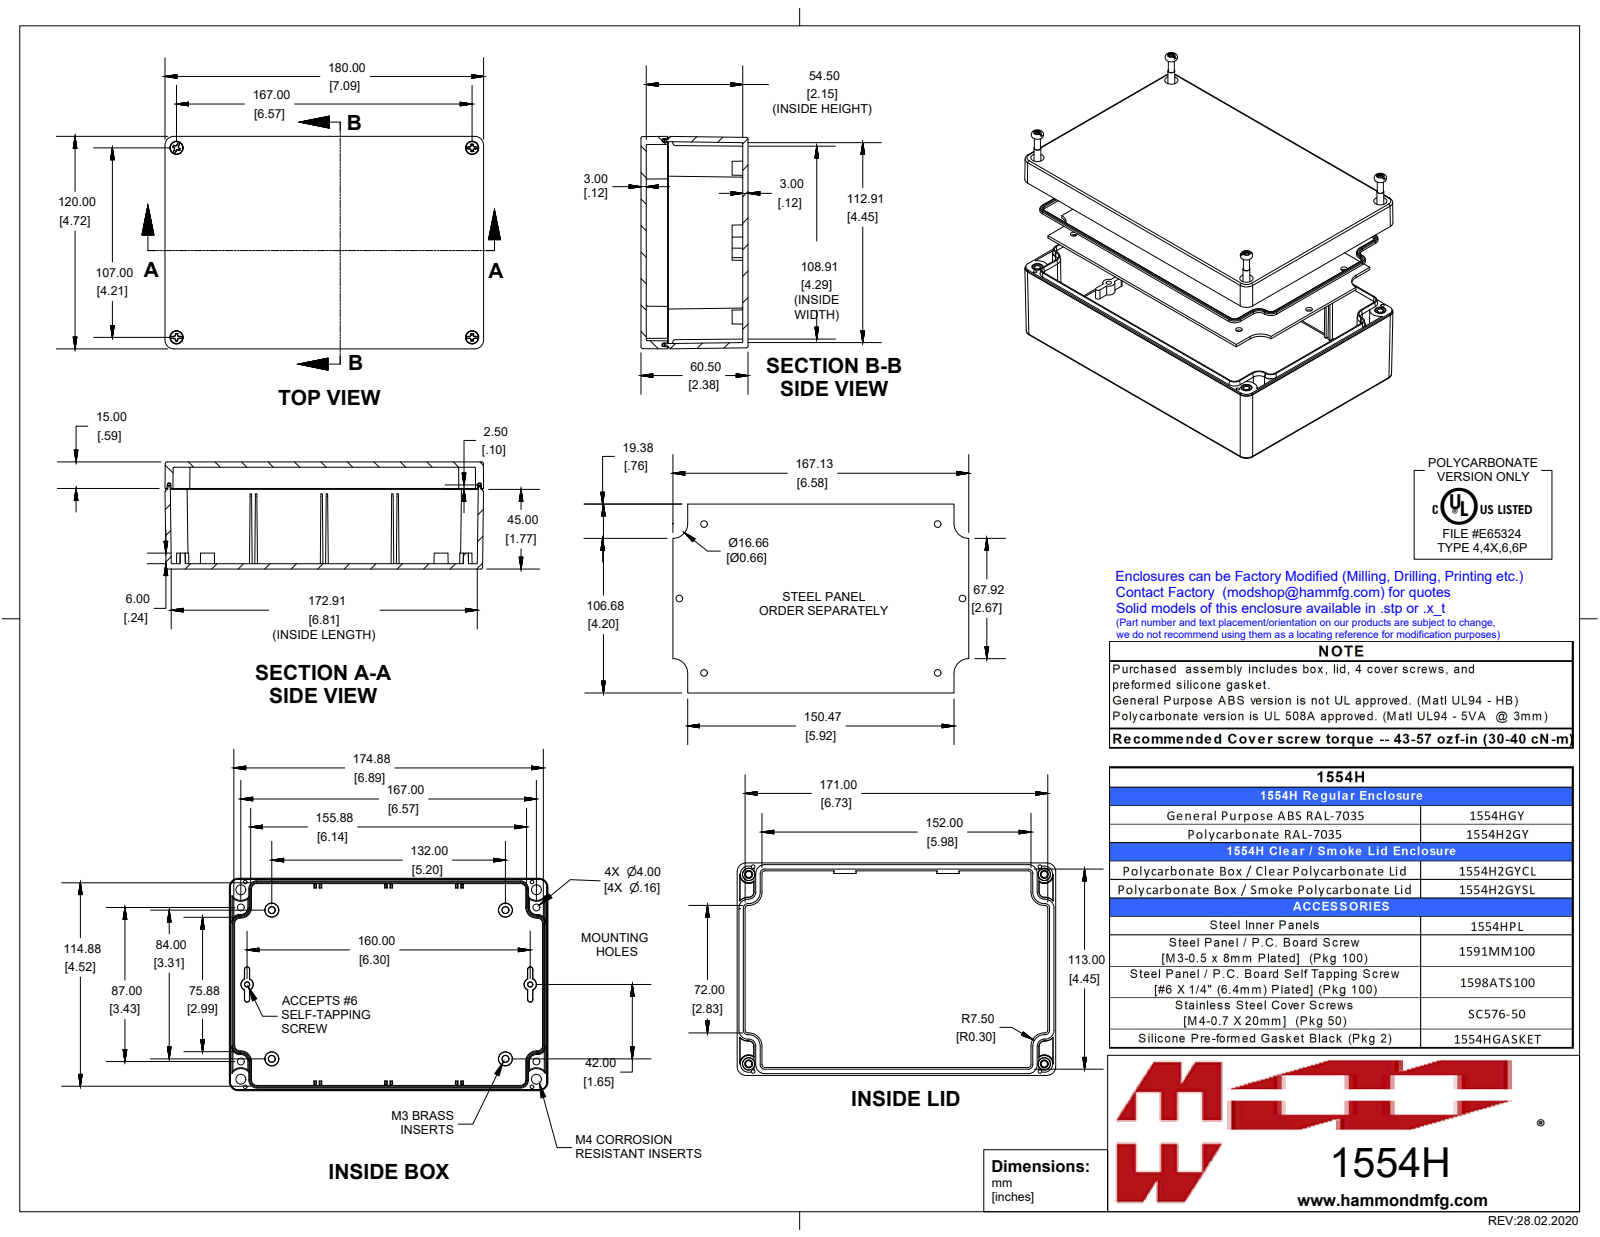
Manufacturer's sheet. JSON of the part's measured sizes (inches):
{"part_name": "1554HGY", "step_written_by": "SolidWorks 2019 (AUTOMOTIVE_DESIGN)", "units": "inches", "bodies": {"solids": 15, "faces": 1364, "planar": 382, "cylindrical": 348, "other": 634}, "overall_size": [7.087, 4.724, 2.382], "volume_in3": 15.21, "surface_area_in2": 278.2, "round_holes": [[0.079, 4], [0.097, 4], [0.128, 4], [0.138, 4], [0.276, 4]], "round_bosses_or_shafts": [[0.25, 4], [0.218, 4], [0.21, 4], [0.19, 4], [0.154, 4], [0.153, 4], [0.15, 4], [0.135, 4]], "partial_cylinders_radius": [[0.02, 44], [0.039, 8], [0.197, 8], [0.187, 4], [0.059, 2]], "face_to_face_distances": [0.118, 2.264, 2.382, 2.146, 0.059, 0.177, 0.492, 0.023, 0.374, 1.791], "hole_center_spacings": [0.197, 0.824, 0.859, 3.822, 3.974, 4.384, 5.821, 5.903]}
